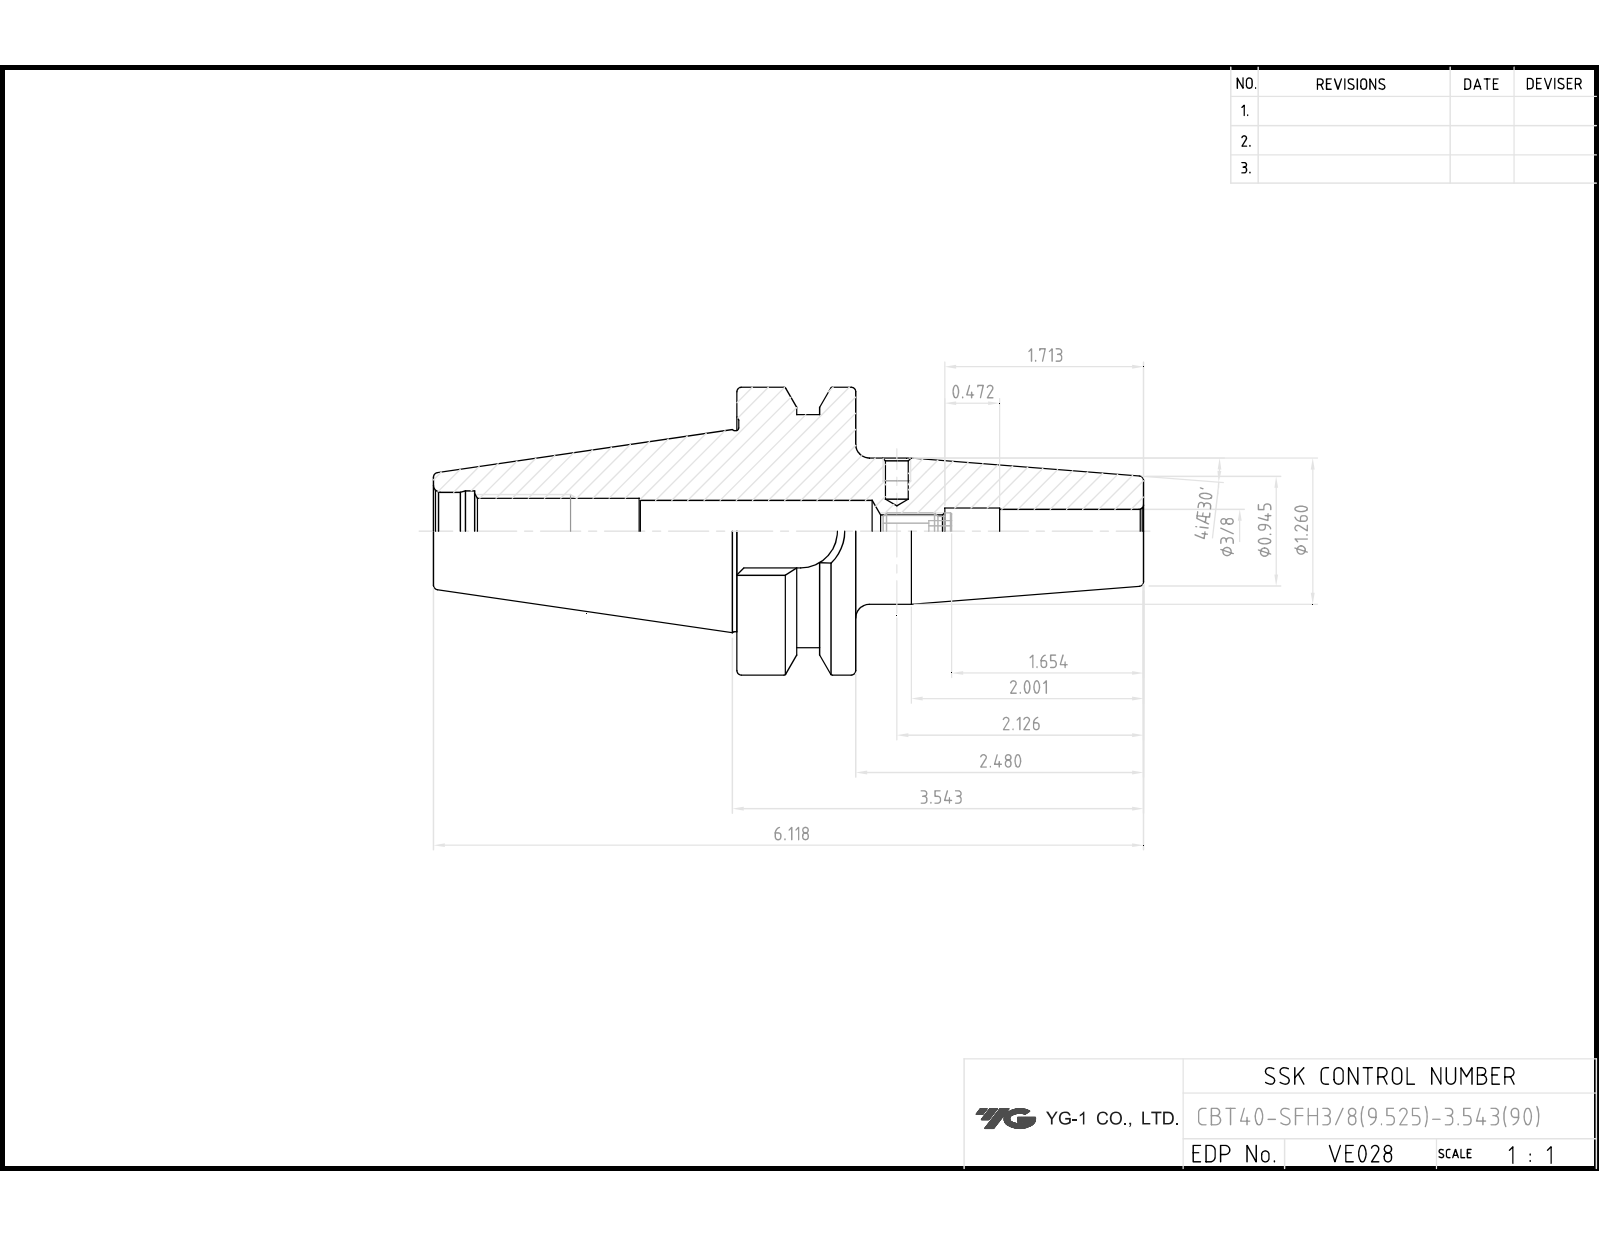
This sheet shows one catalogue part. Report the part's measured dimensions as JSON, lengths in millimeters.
{"part_name": "LO-CBT40-SFH9.525-90", "step_written_by": "Autodesk Inventor 2025 (AUTOMOTIVE_DESIGN)", "units": "millimeters", "bodies": {"solids": 1, "faces": 61, "planar": 24, "cylindrical": 15, "other": 22}, "overall_size": [155.4, 63, 63], "volume_mm3": 159121, "surface_area_mm2": 29484, "round_holes": [[6.92, 1], [9.53, 1], [10.72, 1], [13.84, 1], [17, 1], [17.6, 1]], "round_bosses_or_shafts": [[63, 1], [52.6, 1], [44, 1], [32, 1]], "partial_cylinders_radius": [[8.05, 1]], "face_to_face_distances": [26, 45.2, 89, 63, 0.4, 25.6, 88.6, 16.1, 66.4, 66.8]}
